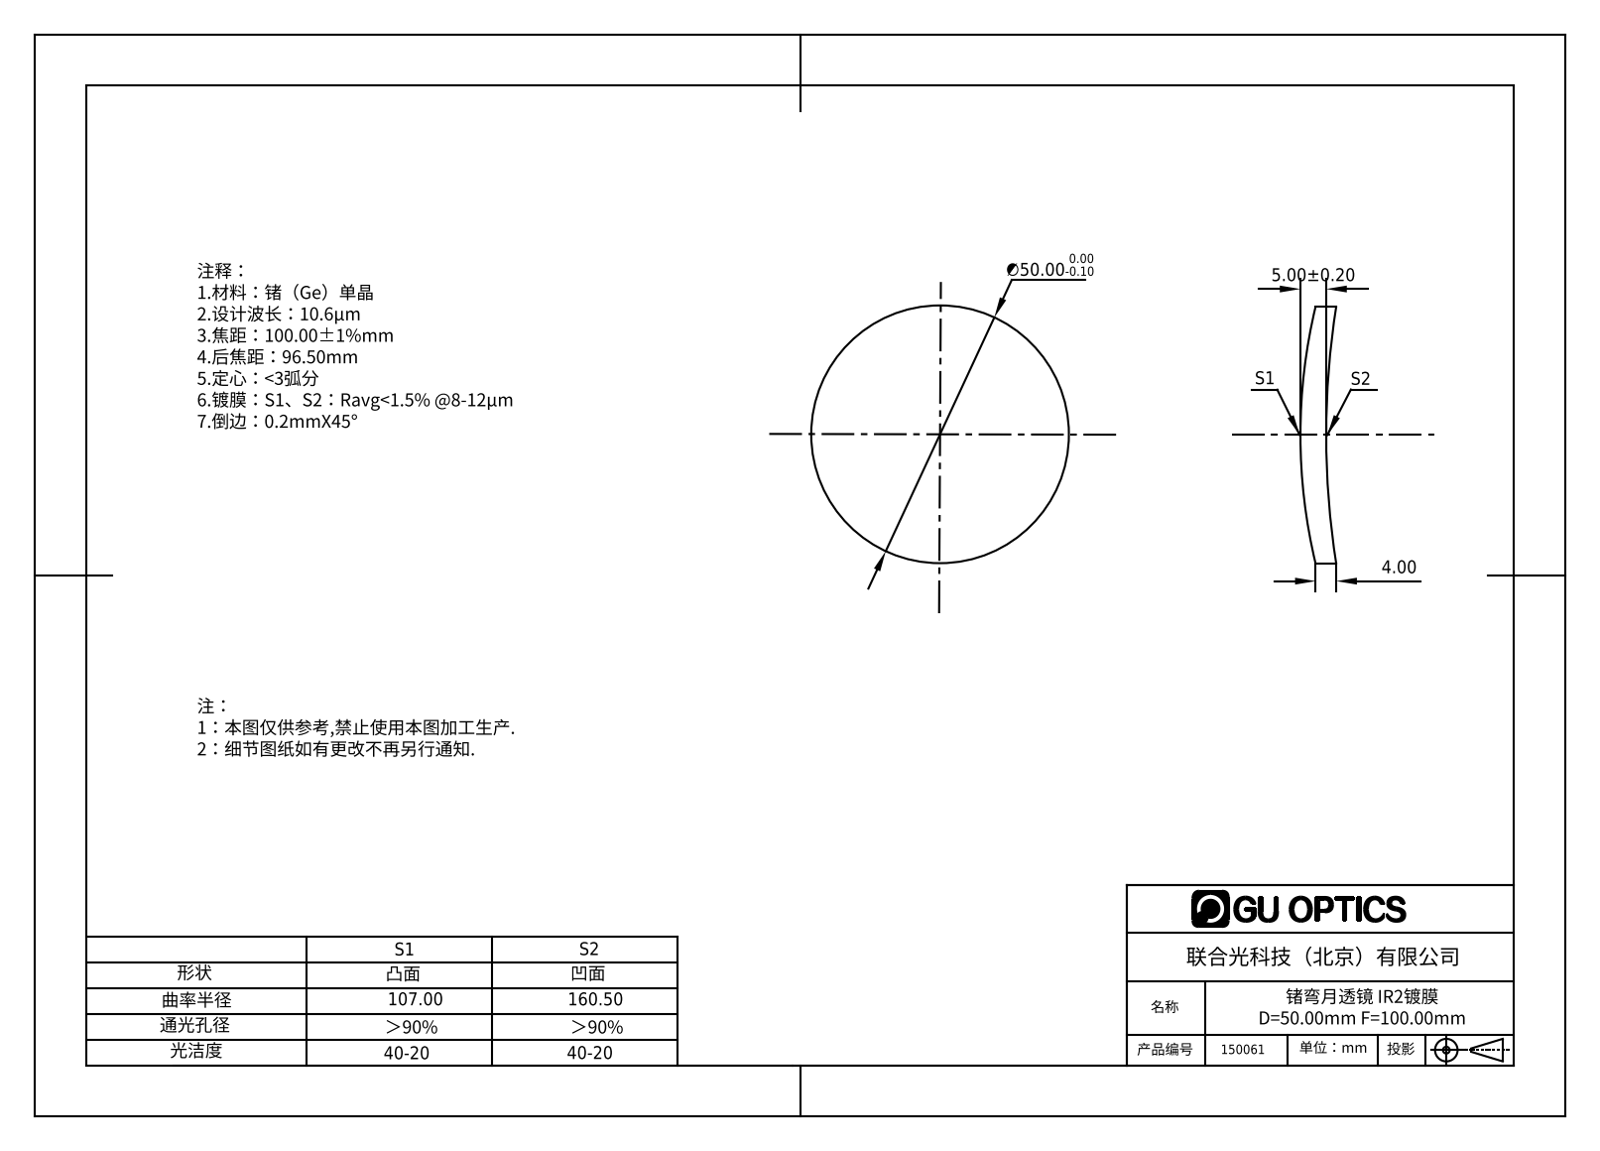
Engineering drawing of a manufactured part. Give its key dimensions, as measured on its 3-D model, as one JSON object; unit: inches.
{"part_name": "150055", "step_written_by": "SolidWorks 2016 (AUTOMOTIVE_DESIGN)", "units": "inches", "bodies": {"solids": 1, "faces": 6, "planar": 0, "cylindrical": 2, "other": 4}, "overall_size": [1.969, 1.969, 0.274], "volume_in3": 0.54, "surface_area_in2": 7.122, "round_bosses_or_shafts": [[1.969, 1]]}
